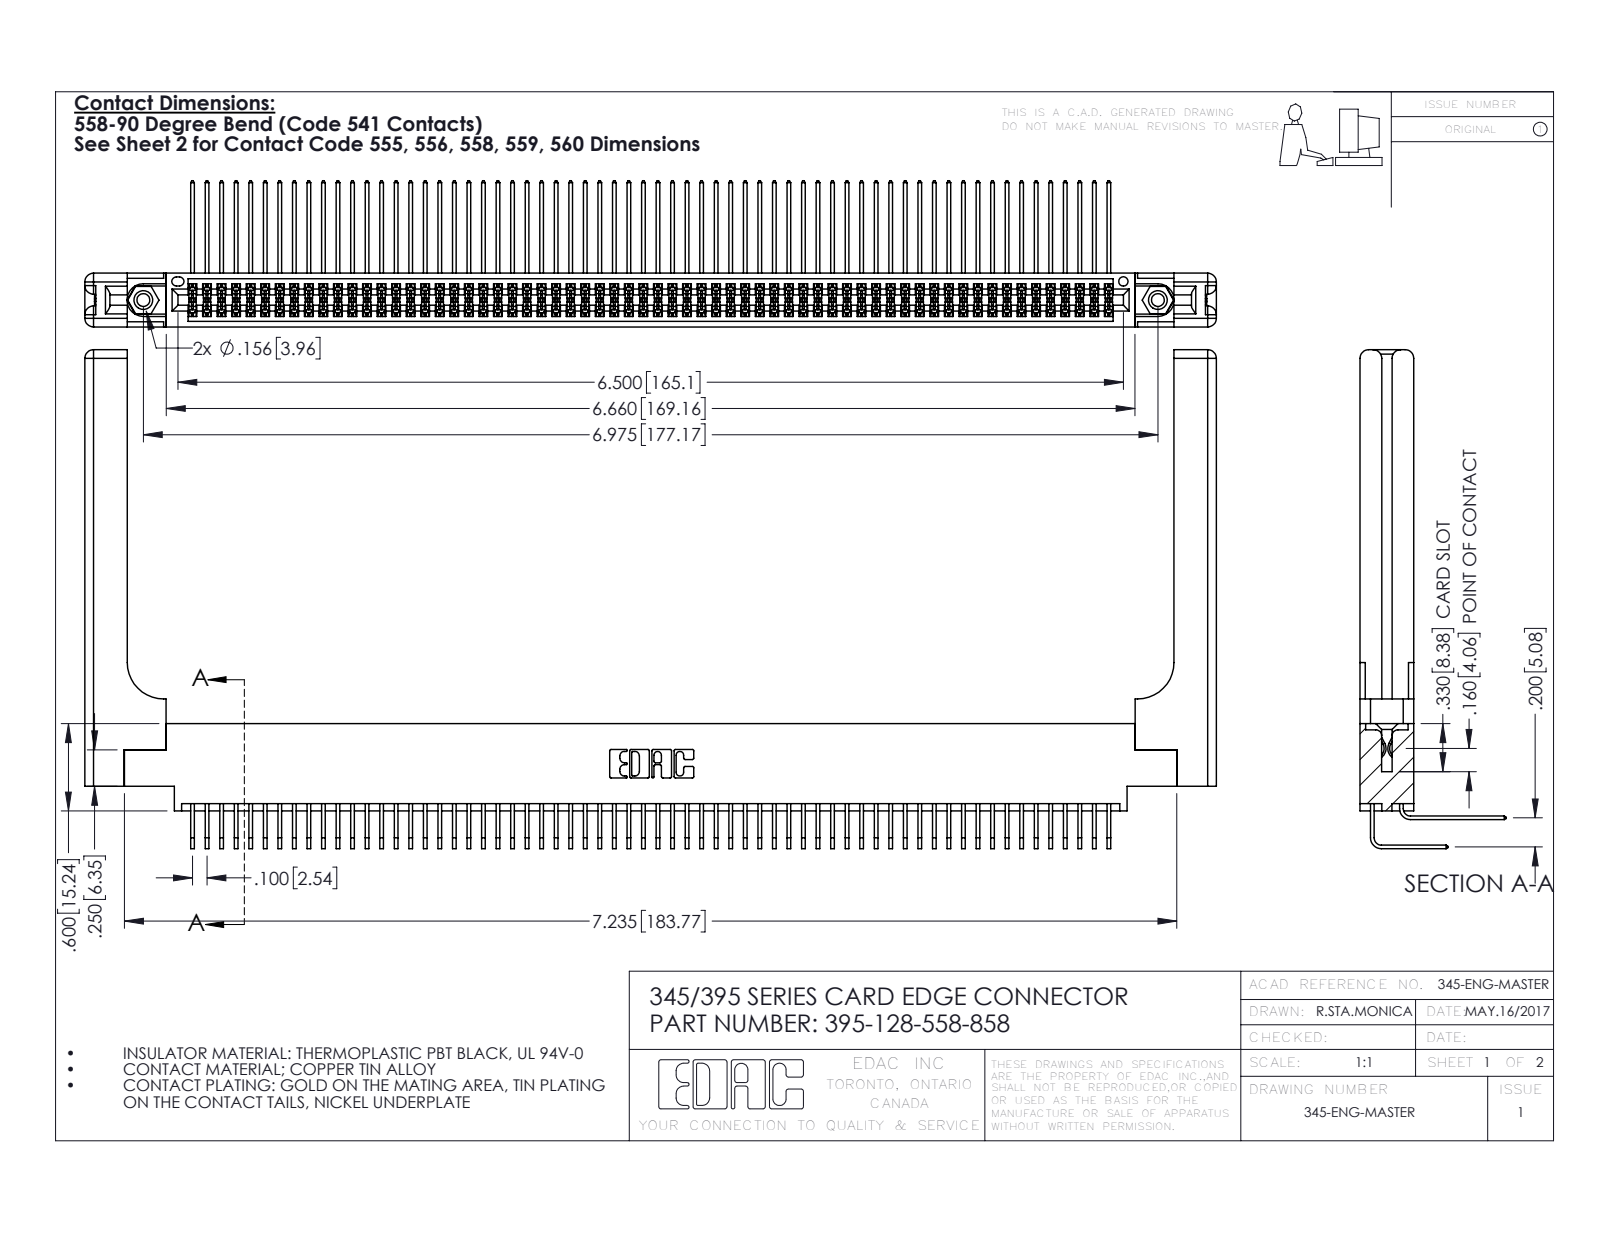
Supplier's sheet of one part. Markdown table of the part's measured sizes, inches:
| quantity | value |
| --- | --- |
| part name | 345-292-001_558 559 Tail - 1; 345 Part_0.170 Offset - 0.156 Dia-TH; 345-250-001_345-250-001-102; 345-220-058_345-220-058 (+2 more) |
| STEP written by | SolidWorks 2016 (CONFIG_CONTROL_DESIGN) |
| units | inches |
| bodies | 133 solids, 7042 faces (4712 planar, 2270 cylindrical, 60 other) |
| overall size | 7.779 × 3.429 × 1.005 |
| volume | 1.739 in³ |
| surface area | 59.98 in² |
| round holes (diameter × count) | 0.089 × 2, 0.125 × 2, 0.156 × 2, 0.064 × 1 |
| round bosses / shafts (diameter × count) | 0.155 × 2 |
| partial cylindrical surfaces (radius × count) | 0.006 × 193, 0.01 × 22, 0.06 × 16, 0.007 × 6, 0.031 × 6, 0.026 × 3, 0.014 × 2, 0.019 × 2 |
| main face-to-face distances | 0.072, 0.298, 0.37, 0.2, 0.098, 0.272, 0.025, 0.225, 0.175, 0.025 |
| hole center spacings | 0.27, 6.739, 6.975 |
